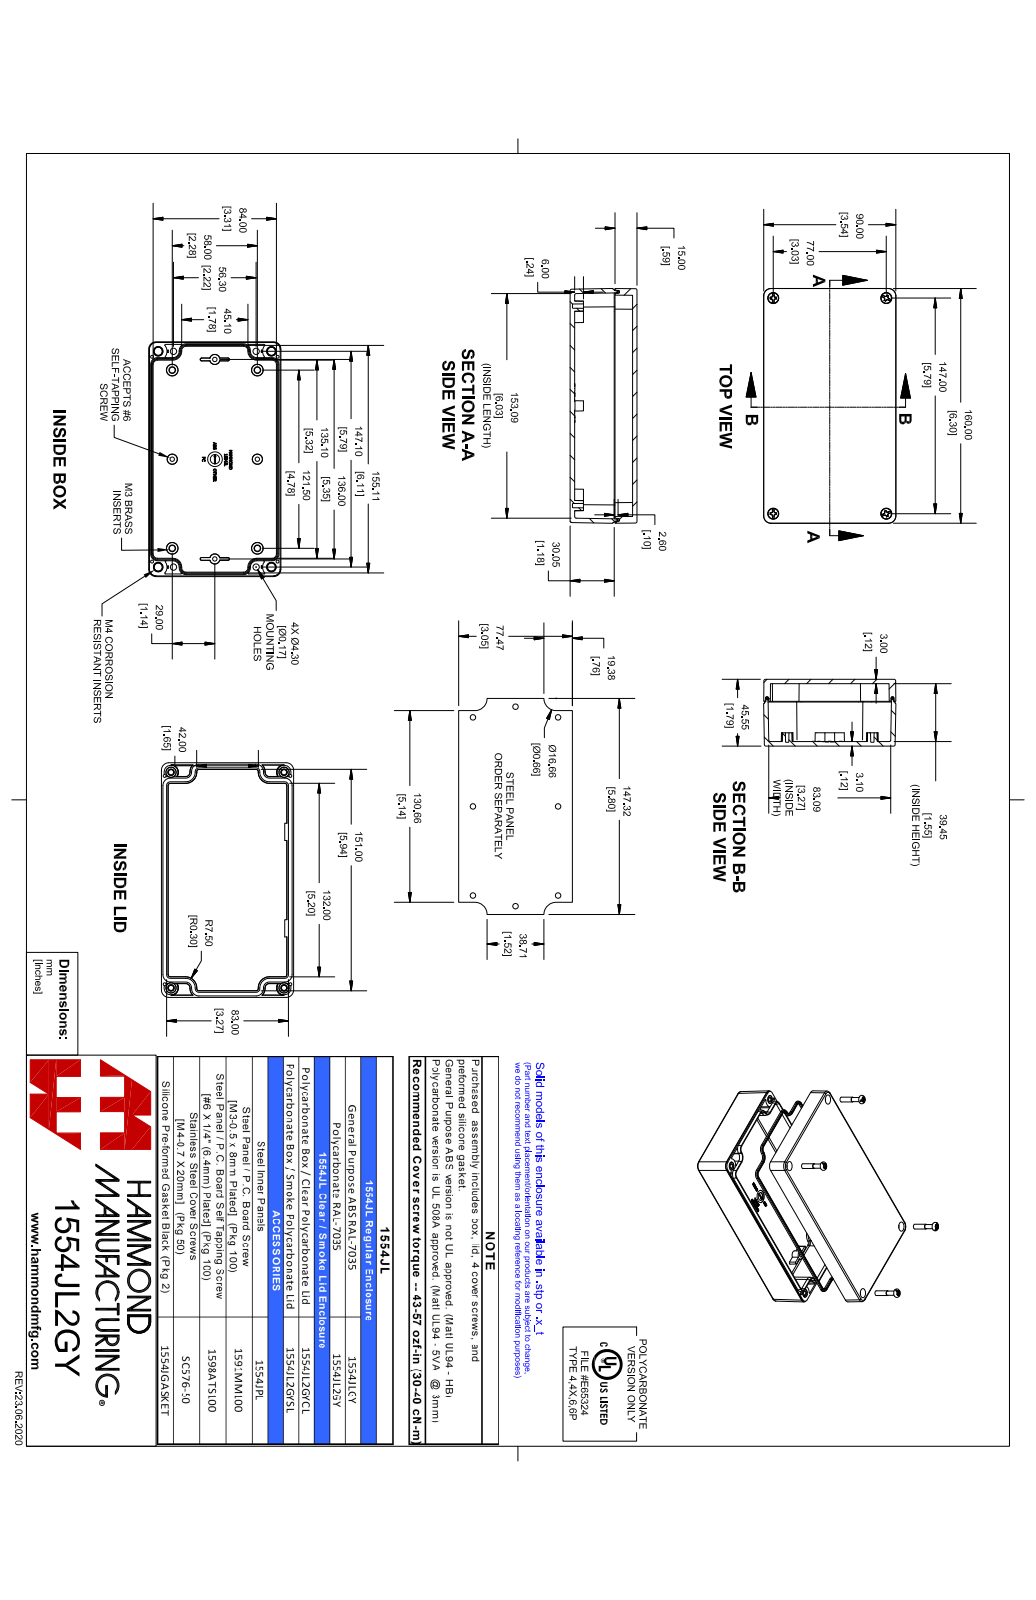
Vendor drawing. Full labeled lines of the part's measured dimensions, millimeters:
Part name (STEP PRODUCT): 1554JL2GY
STEP written by: SolidWorks 2021 (AUTOMOTIVE_DESIGN)
Units: millimetres
Bodies: 15 solids, 1434 faces (366 planar, 321 cylindrical, 747 other)
Overall size (bounding box): 160.1 × 90.1 × 45.5
Volume: 165 200 mm³ · Surface area: 117 500 mm²
Round holes (diameter × count): ⌀2 ×4, ⌀2.5 ×4, ⌀3.3 ×4, ⌀3.5 ×4, ⌀4.6 ×4, ⌀7 ×4
Round bosses / shafts (diameter × count): ⌀6.4 ×4, ⌀5.5 ×4, ⌀5.3 ×4, ⌀4.8 ×4, ⌀3.9 ×4, ⌀3.9 ×4, ⌀3.8 ×4, ⌀3.4 ×4
Partial cylindrical surfaces — rounded edges, fillets, slot ends (radius × count): R1 ×18, R0.5 ×16, R5 ×8, R0.8 ×4, R3 ×4, R4.7 ×4
Main face-to-face distances: 45.5, 3, 42.5, 3.1, 39.4, 42.4, 3, 4.5, 1.5, 12
Hole centre spacings: 5, 15.9, 17.2, 68.7, 72.6, 81.4, 132.5, 134.6
